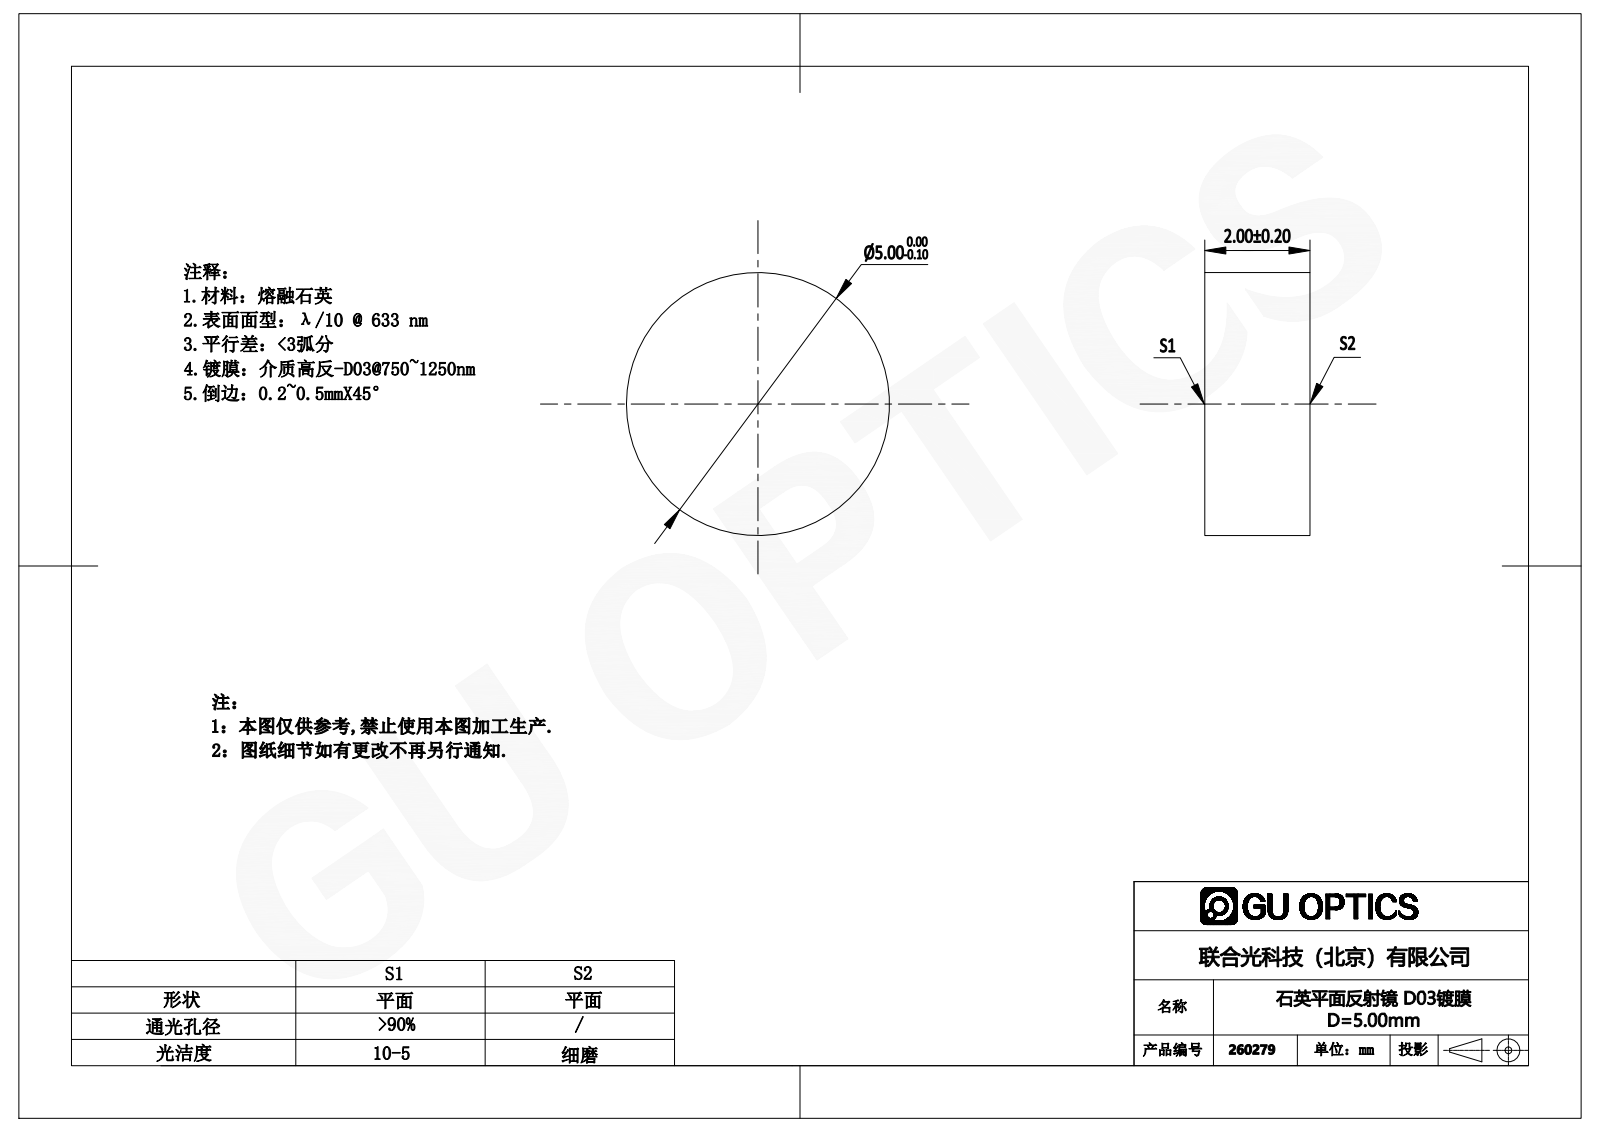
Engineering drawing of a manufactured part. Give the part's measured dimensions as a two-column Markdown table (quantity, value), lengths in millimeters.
| quantity | value |
| --- | --- |
| part name | 260000 |
| STEP written by | SolidWorks 2016 (AUTOMOTIVE_DESIGN) |
| units | millimeters |
| bodies | 1 solid, 4 faces (2 planar, 2 cylindrical, 0 other) |
| overall size | 5 × 5 × 2 |
| volume | 39 mm³ |
| surface area | 71 mm² |
| round bosses / shafts (diameter × count) | 5 × 1 |
| main face-to-face distances | 2 |
